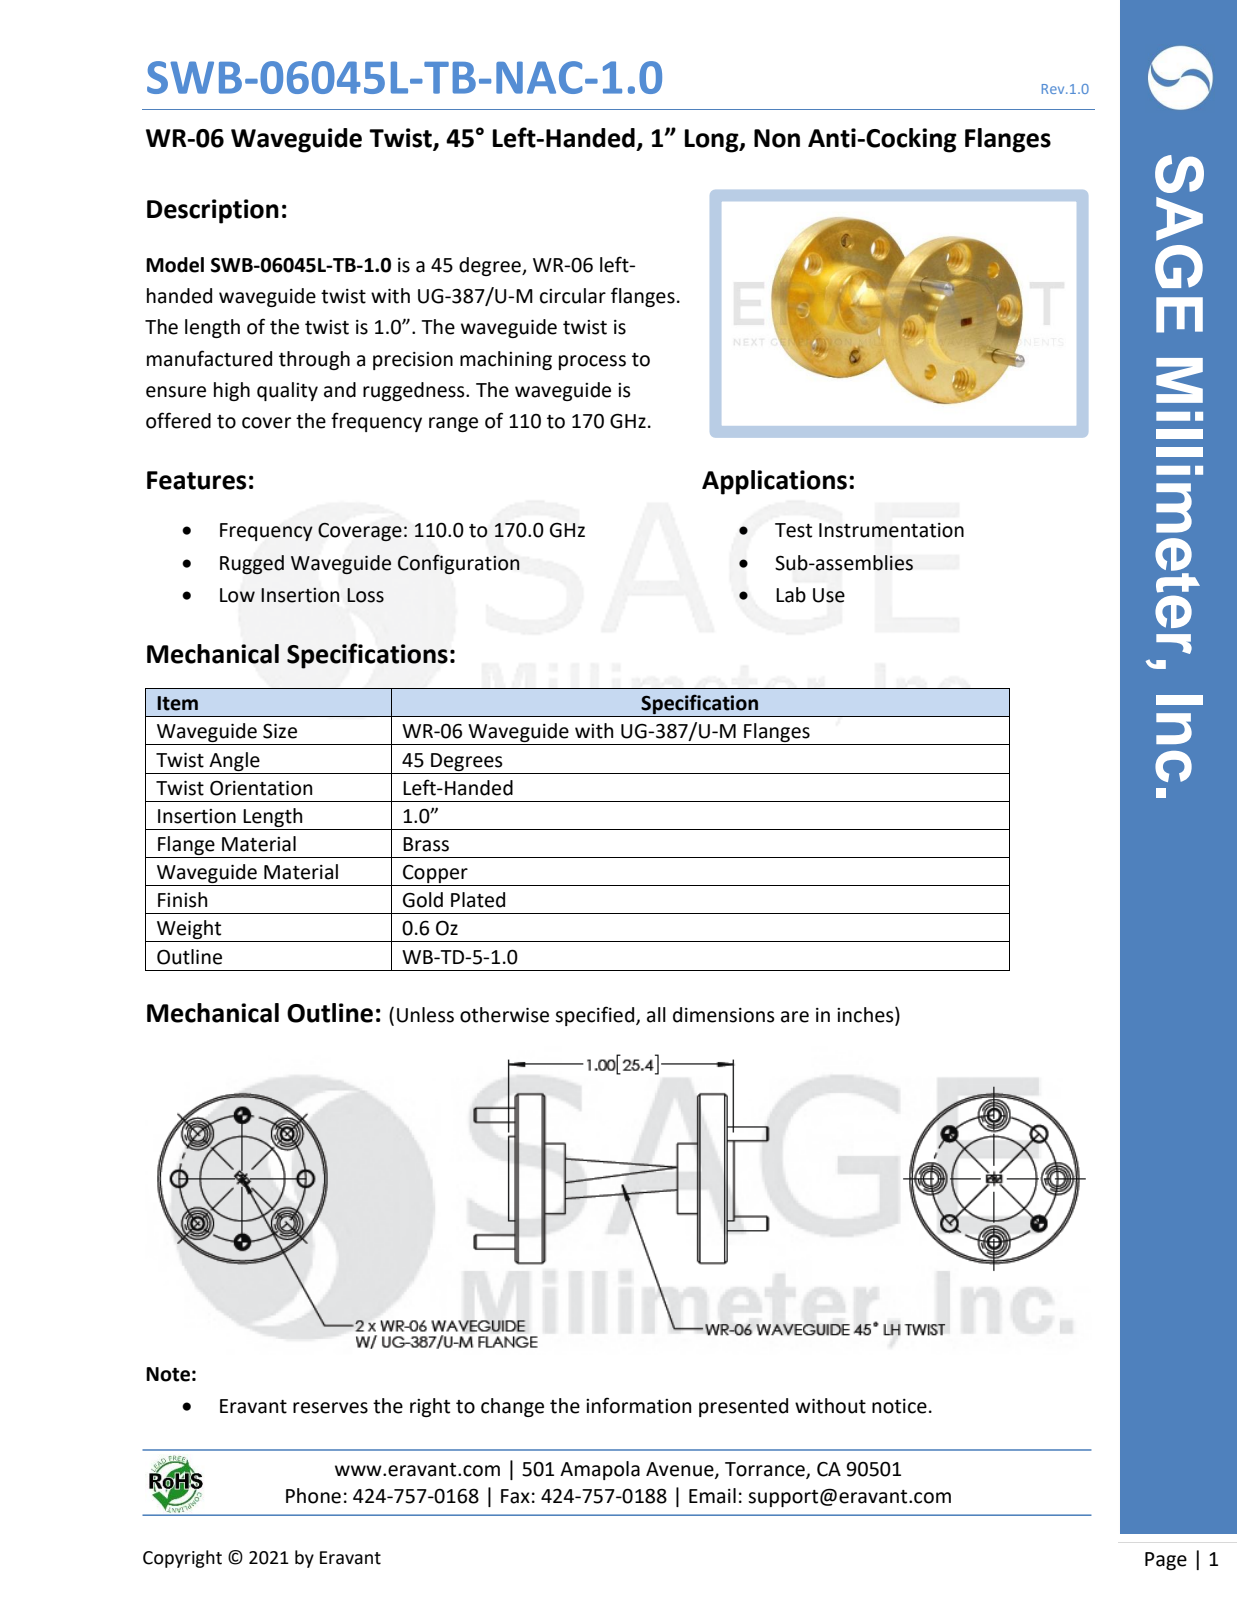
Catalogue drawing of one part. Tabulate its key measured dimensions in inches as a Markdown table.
| quantity | value |
| --- | --- |
| part name | SWB-06045L-TB-1.0 |
| STEP written by | SolidWorks 2016 (AUTOMOTIVE_DESIGN) |
| units | inches |
| bodies | 5 solids, 146 faces (34 planar, 68 cylindrical, 44 other) |
| overall size | 1.305 × 0.75 × 0.75 |
| volume | 0.134 in³ |
| surface area | 3.412 in² |
| round holes (diameter × count) | 0.089 × 8, 0.14 × 8, 0.061 × 4, 0.067 × 4 |
| round bosses / shafts (diameter × count) | 0.063 × 4, 0.75 × 1, 0.375 × 1, 0.31 × 1 |
| main face-to-face distances | 0.68, 0.81, 0.13, 0.13, 0.81, 0.94, 0.03, 0.97, 0.25, 0.75 |
| hole center spacings | 0.398, 0.519, 0.215, 0.562, 0.215, 0.397, 0.52, 0.562 |
